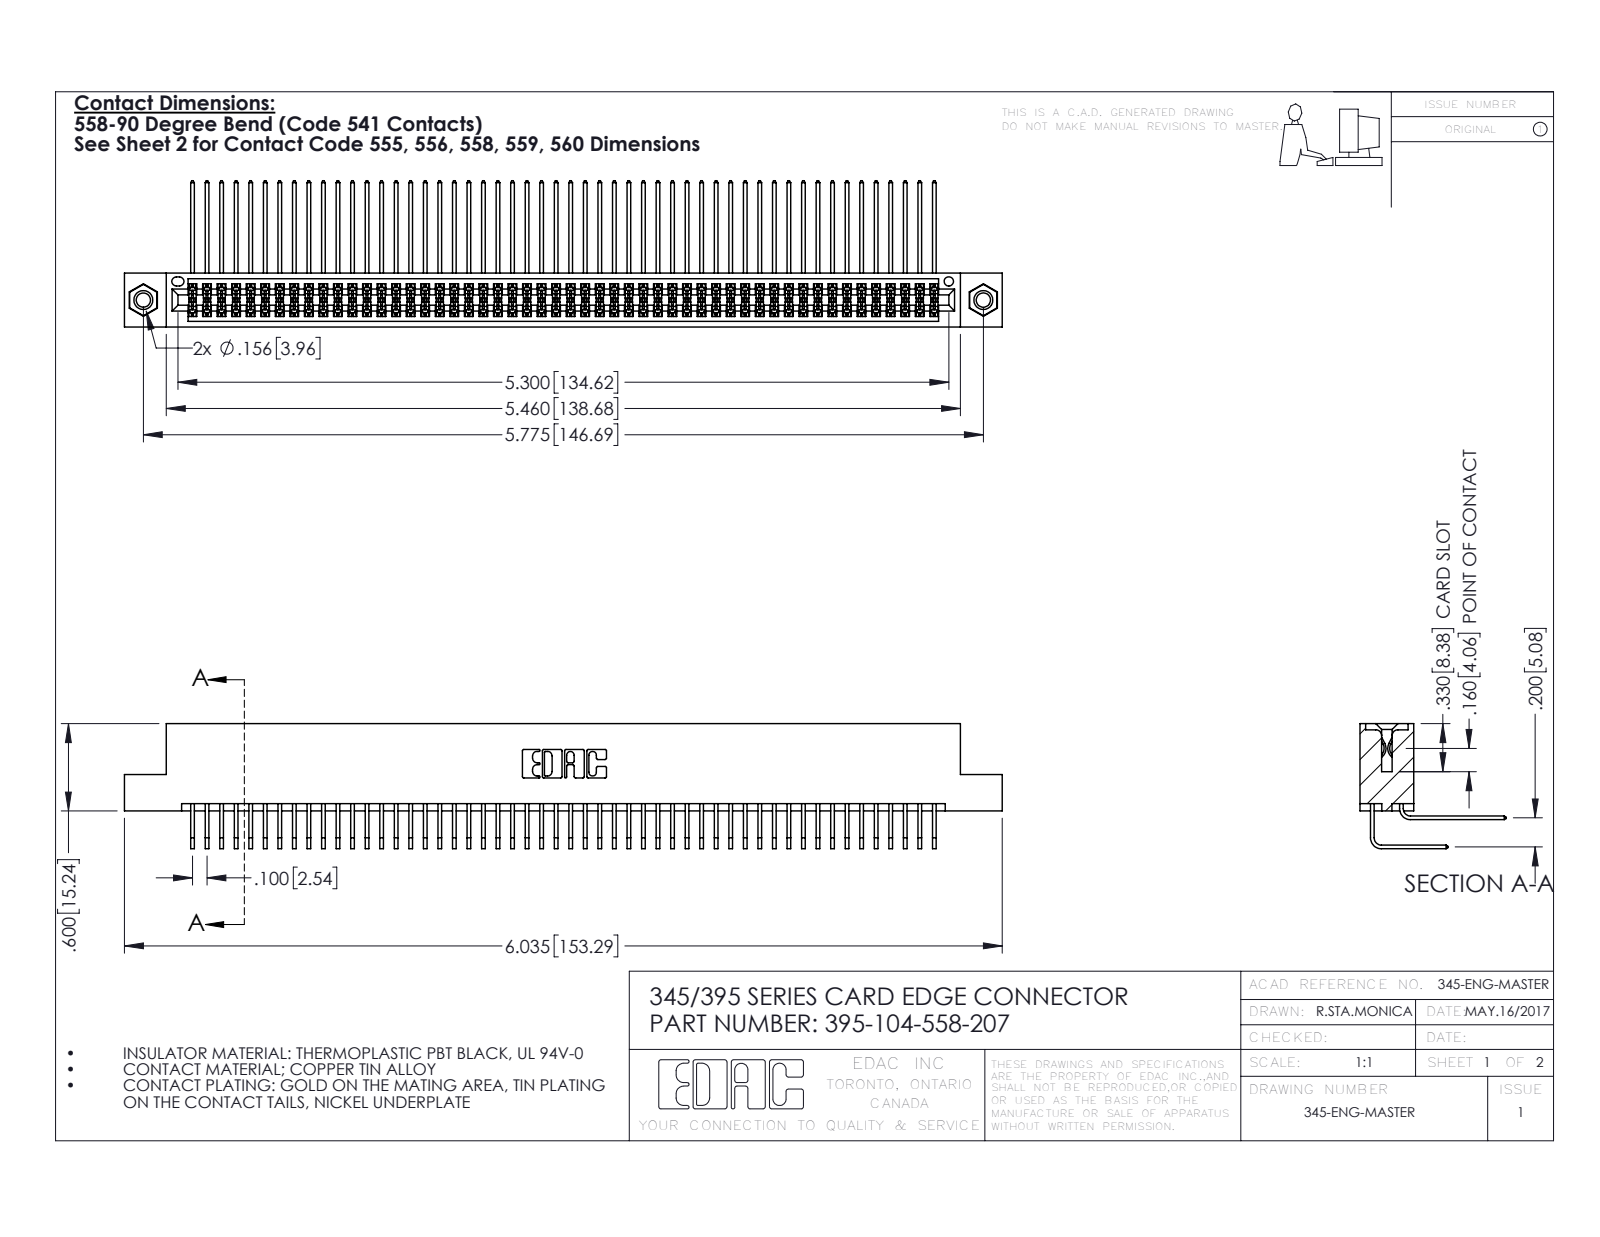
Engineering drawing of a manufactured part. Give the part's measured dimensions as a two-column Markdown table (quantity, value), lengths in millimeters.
| quantity | value |
| --- | --- |
| part name | 345-292-001_558 Tail - 2; 395-104-558-207; 345-250-001_345-250-005-103; 345 Part_Flush Mounting Lugs - 0.156 Dia-TI (+1 more) |
| STEP written by | SolidWorks 2016 (CONFIG_CONTROL_DESIGN) |
| units | millimeters |
| bodies | 107 solids, 5594 faces (3752 planar, 1826 cylindrical, 16 other) |
| overall size | 153.3 × 25.5 × 21.8 |
| volume | 15 600 mm³ |
| surface area | 26 060 mm² |
| round holes (diameter × count) | 2.5 × 2, 3.2 × 2, 4 × 2, 1.6 × 1 |
| round bosses / shafts (diameter × count) | 3.9 × 2 |
| partial cylindrical surfaces (radius × count) | 0.2 × 157, 0.3 × 22, 0.2 × 6, 0.8 × 6, 0.7 × 3, 0.4 × 2, 0.5 × 2, 0.6 × 2 |
| main face-to-face distances | 1.8, 7.6, 5.1, 9.4, 2.5, 6.9, 0.6, 5.7, 0.6, 4.4 |
| hole center spacings | 6.9, 140.7, 146.7 |
